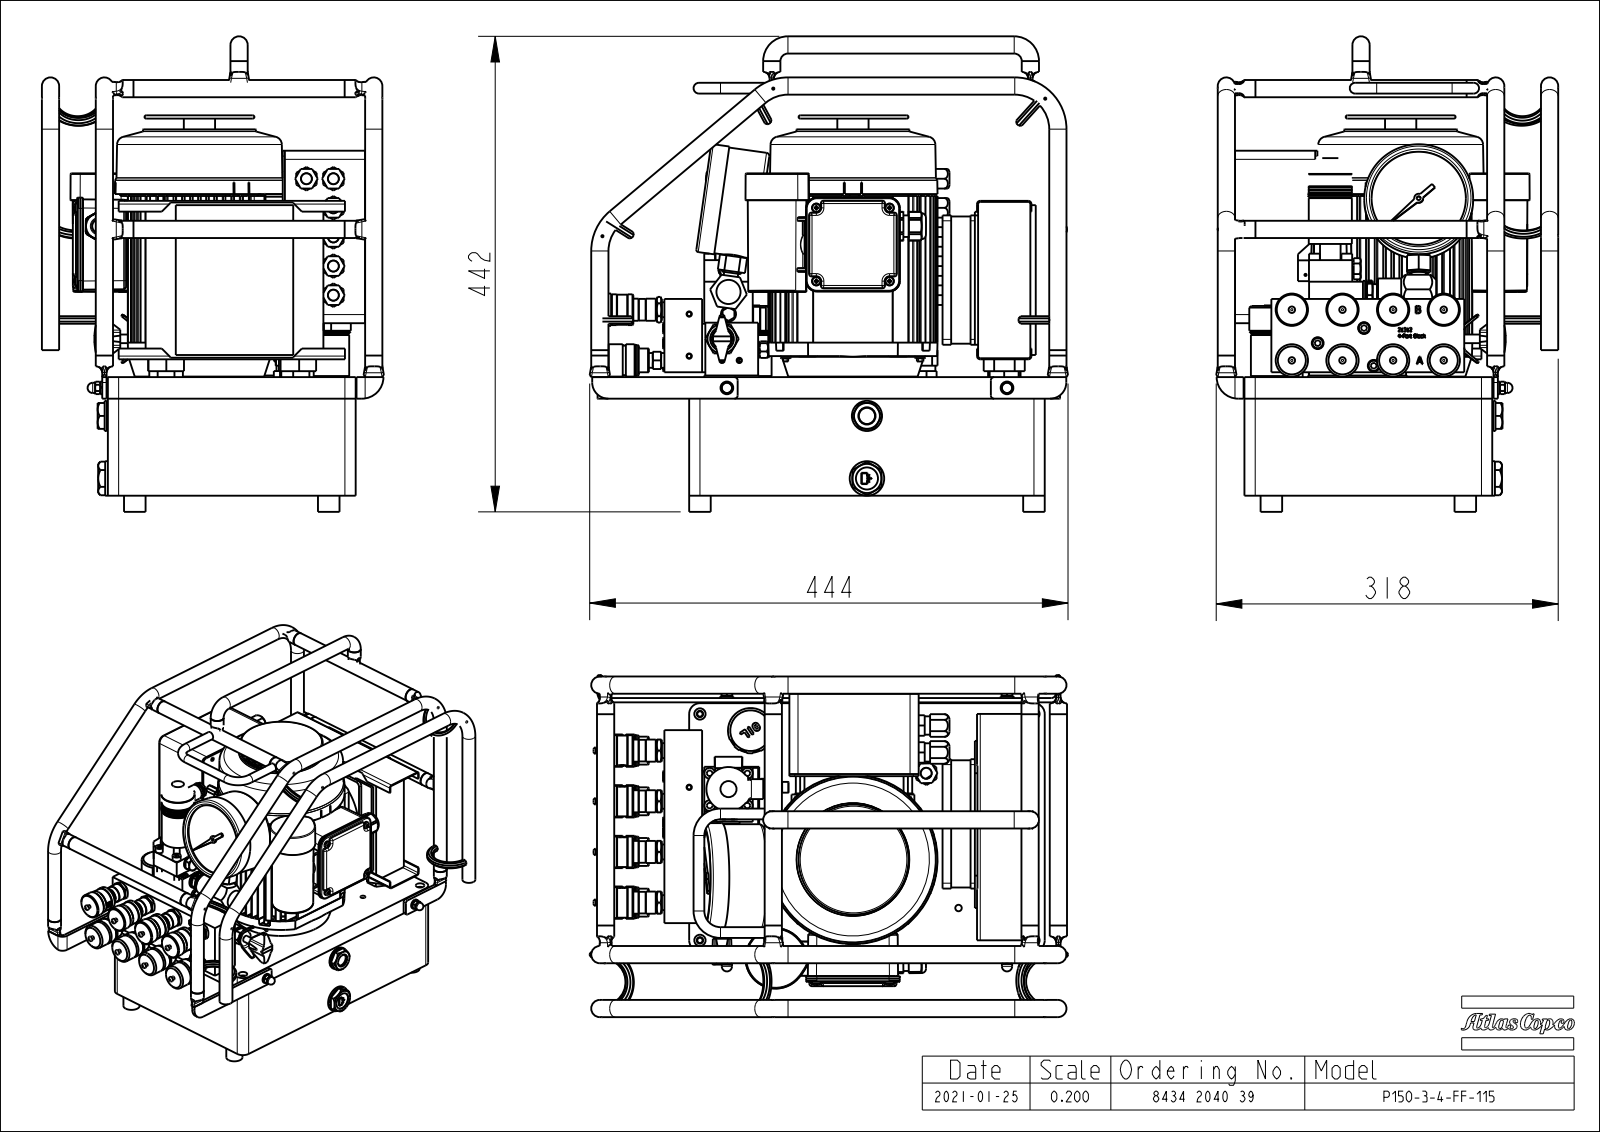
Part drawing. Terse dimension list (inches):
name: ASM0009_SW0001
written by: CREO PARAMETRIC BY PTC INC, 2018100 (CONFIG_CONTROL_DESIGN)
unit: in
bodies: 11 solids, 11692 faces (4532 planar, 3268 cylindrical, 3892 other)
size: 17.616 × 17.366 × 12.82
volume: 506.6 in³; area: 3 413 in²
holes: 25× ⌀0.157, 22× ⌀0.276, 19× ⌀0.118, 16× ⌀0.256, 16× ⌀0.472, 15× ⌀0.194, 13× ⌀0.039, 12× ⌀0.197, 12× ⌀0.394, 12× ⌀0.413, 11× ⌀0.079, 11× ⌀0.236
bosses: 41× ⌀0.394, 23× ⌀0.236, 21× ⌀0.63, 13× ⌀1.181, 10× ⌀0.551, 10× ⌀0.465, 8× ⌀1.125, 8× ⌀0.807
rounds: 244× R0.008, 228× R0.02, 150× R0.039, 84× R0.077, 46× R0.315, 45× R0.197, 44× R0.022, 36× R0.03
face distances: 0.118, 0.197, 4.213, 4.331, 4.016, 4.134, 9.063, 0.157, 0.217, 8.846
hole spacings: 1.969, 3.612, 1.222, 2.085, 3.122, 1.221, 1.222, 2.166
